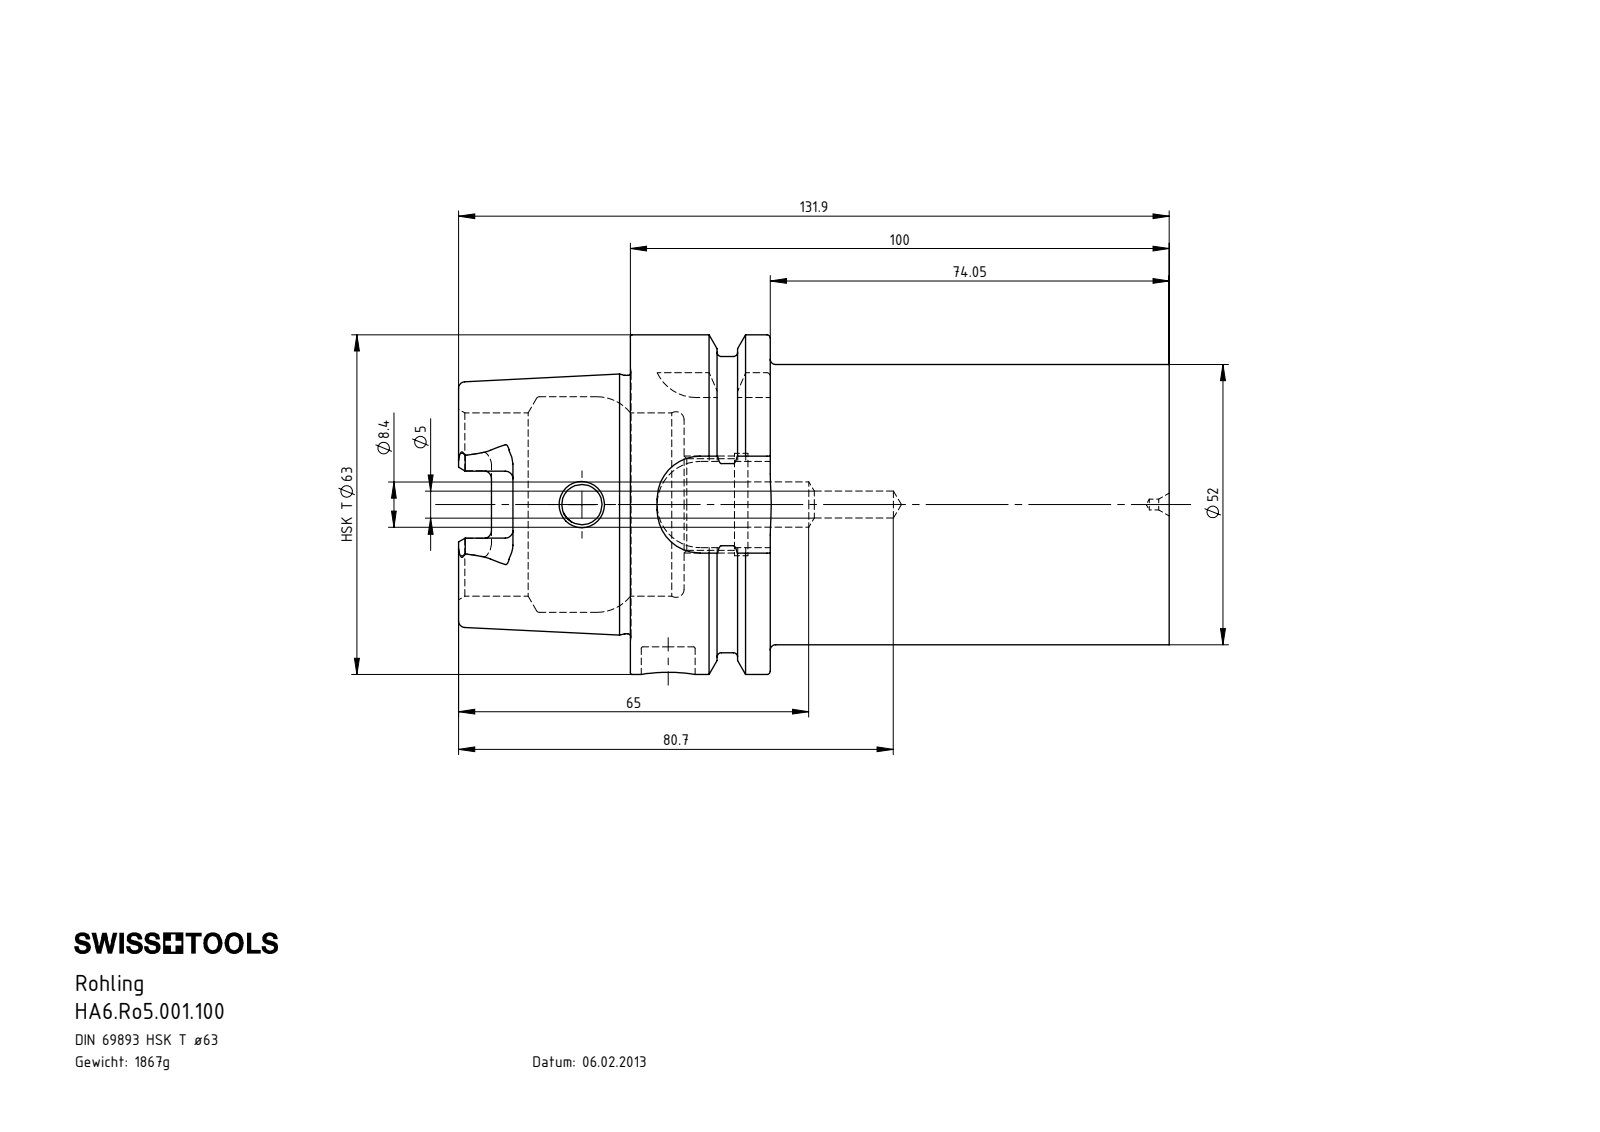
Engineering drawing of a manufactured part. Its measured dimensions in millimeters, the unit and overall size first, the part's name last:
Units: millimetres
Overall size (bounding box): 131.9 × 63 × 63
Round holes (diameter × count): ⌀2 ×1, ⌀5 ×1, ⌀7.5 ×1, ⌀8.4 ×1, ⌀10 ×1, ⌀17 ×1, ⌀19 ×1, ⌀34 ×1, ⌀40 ×1
Round bosses / shafts (diameter × count): ⌀63 ×1, ⌀54.95 ×1, ⌀52 ×1, ⌀47.94 ×1
Partial cylindrical surfaces — rounded edges, fillets, slot ends (radius × count): R1.4 ×6, R2.88 ×4, R8 ×4
Main face-to-face distances: 100, 25.95, 74.05, 16, 9.95, 90.05, 31.9, 41.85, 57.85, 131.9
Volume: 237 854 mm³ · Surface area: 34 816 mm²
Bodies: 1 solid, 120 faces (43 planar, 33 cylindrical, 44 other)
Part name (STEP PRODUCT): HA6.Ro5.001.100
STEP written by: SolidWorks 2017 (AUTOMOTIVE_DESIGN)
